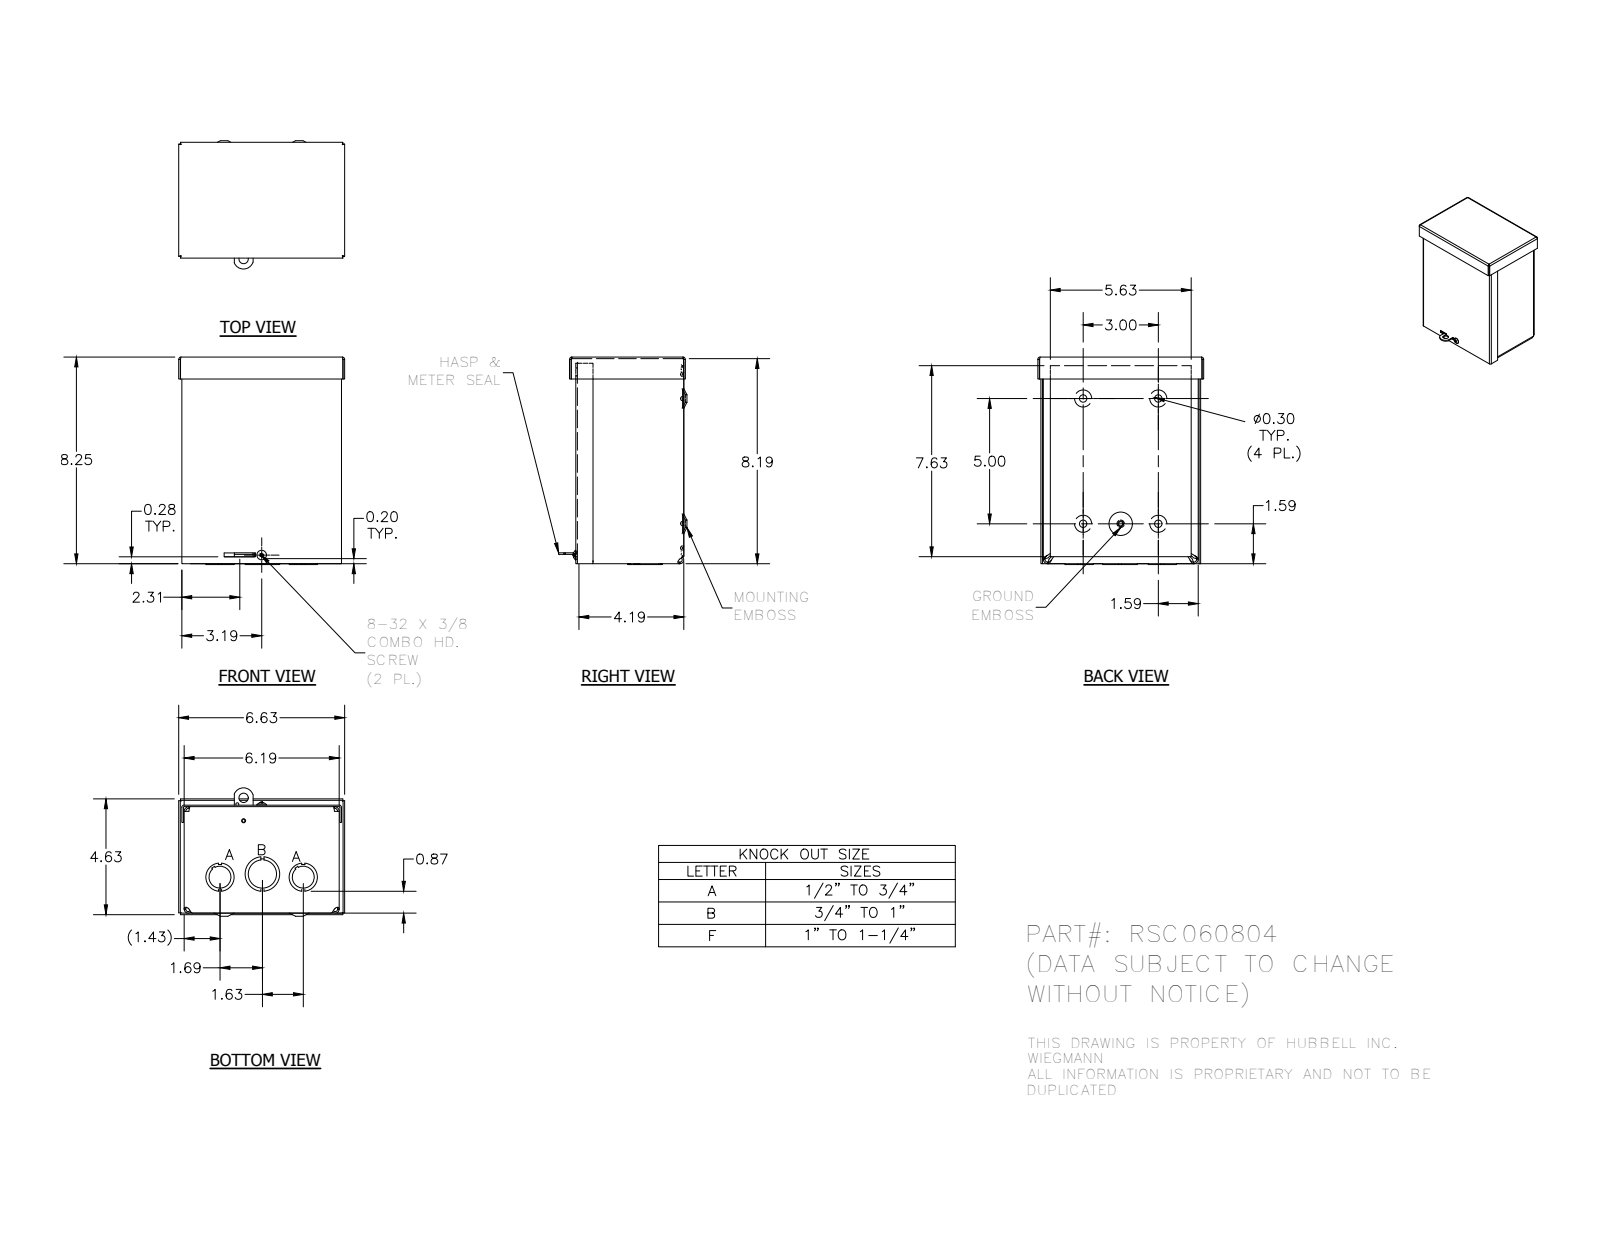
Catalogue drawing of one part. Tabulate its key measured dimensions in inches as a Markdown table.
| quantity | value |
| --- | --- |
| part name | RSC060804; RSC060804_WRAP; RSC0608_LID; RSC0604_CAP (+4 more) |
| STEP written by | Autodesk Inventor 2012 (AUTOMOTIVE_DESIGN) |
| units | inches |
| bodies | 6 solids, 461 faces (220 planar, 116 cylindrical, 125 other) |
| overall size | 8.281 × 6.625 × 5.125 |
| volume | 19.1 in³ |
| surface area | 628.6 in² |
| round holes (diameter × count) | 0.3 × 4, 1.125 × 3, 0.125 × 2, 0.313 × 2, 0.875 × 2, 0.148 × 1, 0.156 × 1, 0.165 × 1, 0.375 × 1, 1.375 × 1 |
| round bosses / shafts (diameter × count) | 0.384 × 1, 0.229 × 1, 0.164 × 1 |
| partial cylindrical surfaces (radius × count) | 0.01 × 10, 0.031 × 8, 0.093 × 8, 0.125 × 8, 0.187 × 8, 0.021 × 4, 0.031 × 4, 0.055 × 4 |
| main face-to-face distances | 0.062, 0.062, 6.126, 4.249, 4.187, 0.063, 8.126, 0.124, 4.312, 4.25 |
| hole center spacings | 1.5, 3, 5, 5.22, 5.831, 0.358, 0.702, 0.913 |
